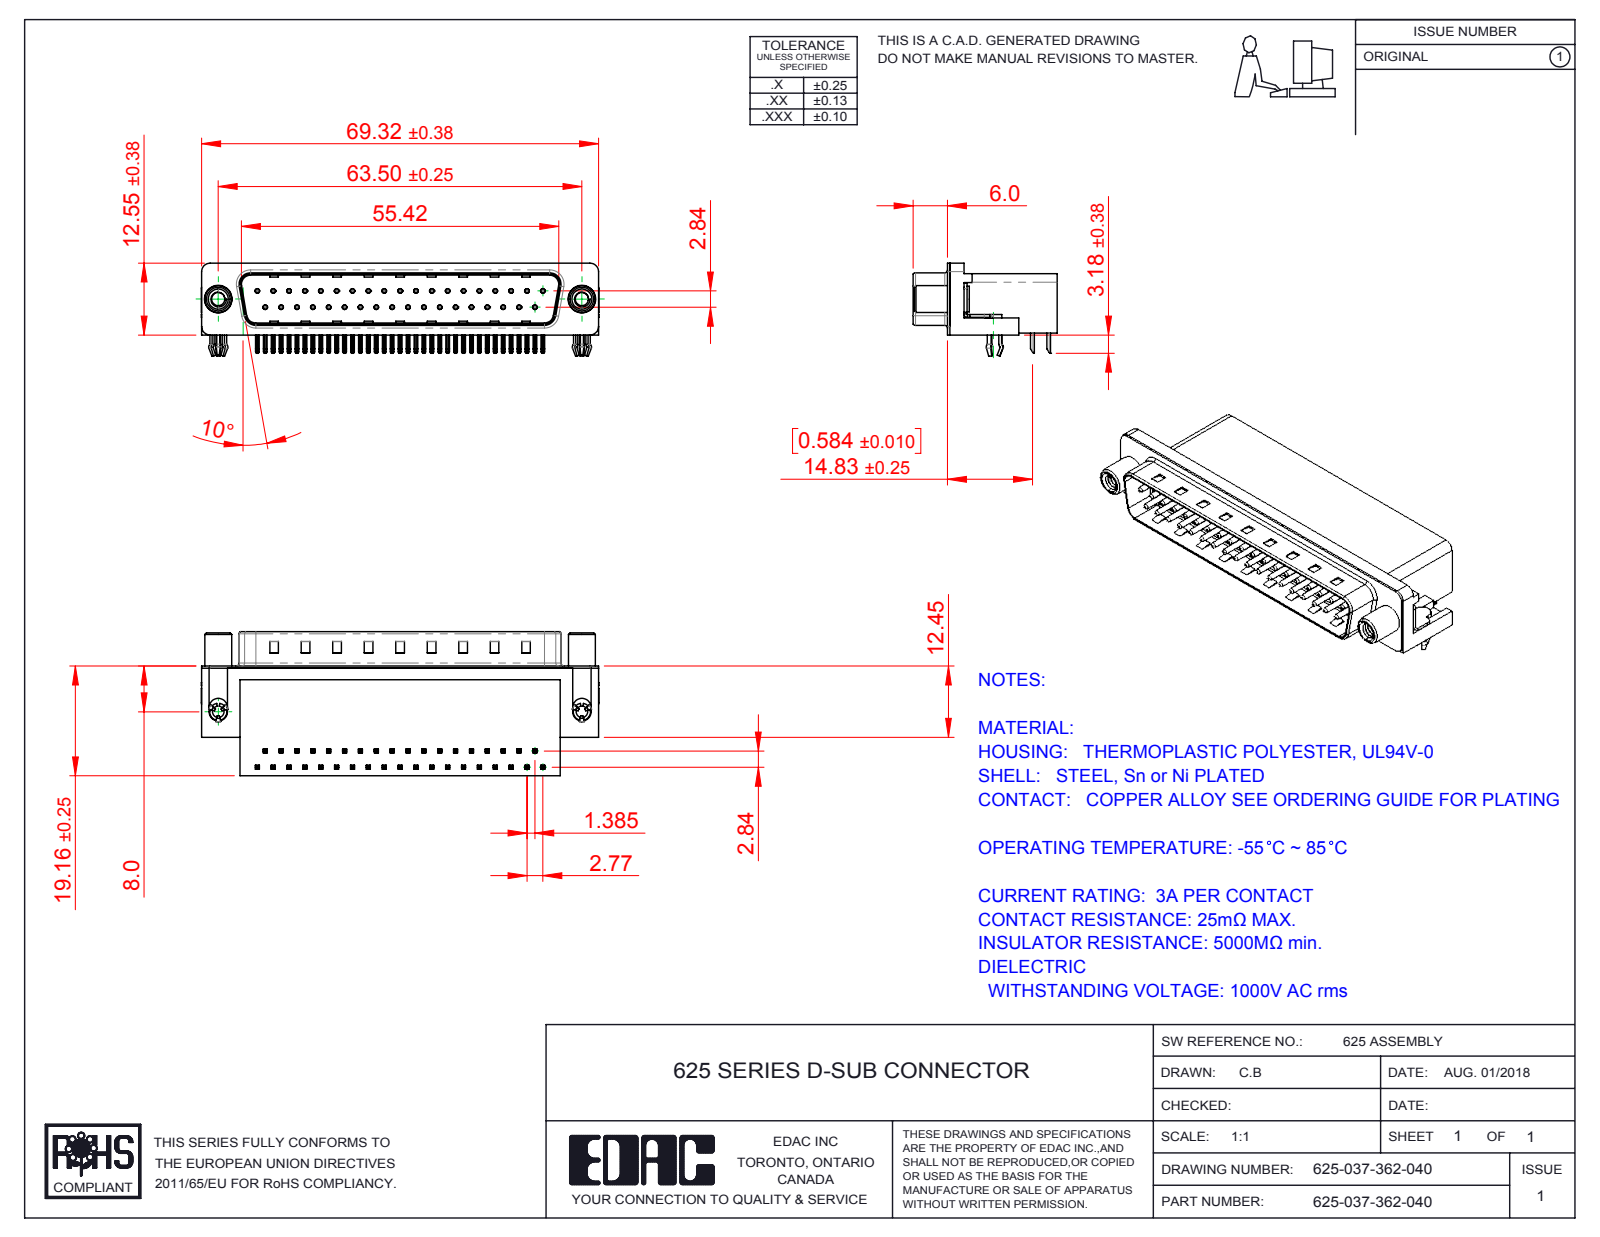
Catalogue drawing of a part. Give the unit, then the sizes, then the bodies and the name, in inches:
Units: inches
Overall size (bounding box): 2.732 × 0.991 × 0.64
Round holes (diameter × count): ⌀0.014 ×37, ⌀0.031 ×37, ⌀0.079 ×2, ⌀0.091 ×2, ⌀0.122 ×2, ⌀0.157 ×2, ⌀0.189 ×2, ⌀0.197 ×2
Round bosses / shafts (diameter × count): ⌀0.03 ×37, ⌀0.193 ×2, ⌀0.185 ×2, ⌀0.177 ×2, ⌀0.152 ×2, ⌀0.118 ×2
Partial cylindrical surfaces — rounded edges, fillets, slot ends (radius × count): R0.01 ×152, R0.005 ×74, R0.039 ×16, R0.02 ×9, R0.063 ×8, R0.059 ×7, R0.035 ×4, R0.079 ×4
Main face-to-face distances: 0.407, 0.016, 0.739, 0.345, 0.112, 0.754, 0.082, 0.398, 0.069, 0.329
Hole centre spacings: 0.124, 0.109, 0.218, 0.327, 0.436, 0.545, 0.763, 0.872
Volume: 0.775 in³ · Surface area: 18.62 in²
Bodies: 43 solids, 3299 faces (2043 planar, 931 cylindrical, 325 other)
Part name (STEP PRODUCT): 625 Housing_37 Socket; 625 Contact Bottom; 625-037-362-040; 625 3 Prong Board Lock (+3 more)
STEP written by: SolidWorks 2016 (CONFIG_CONTROL_DESIGN)
